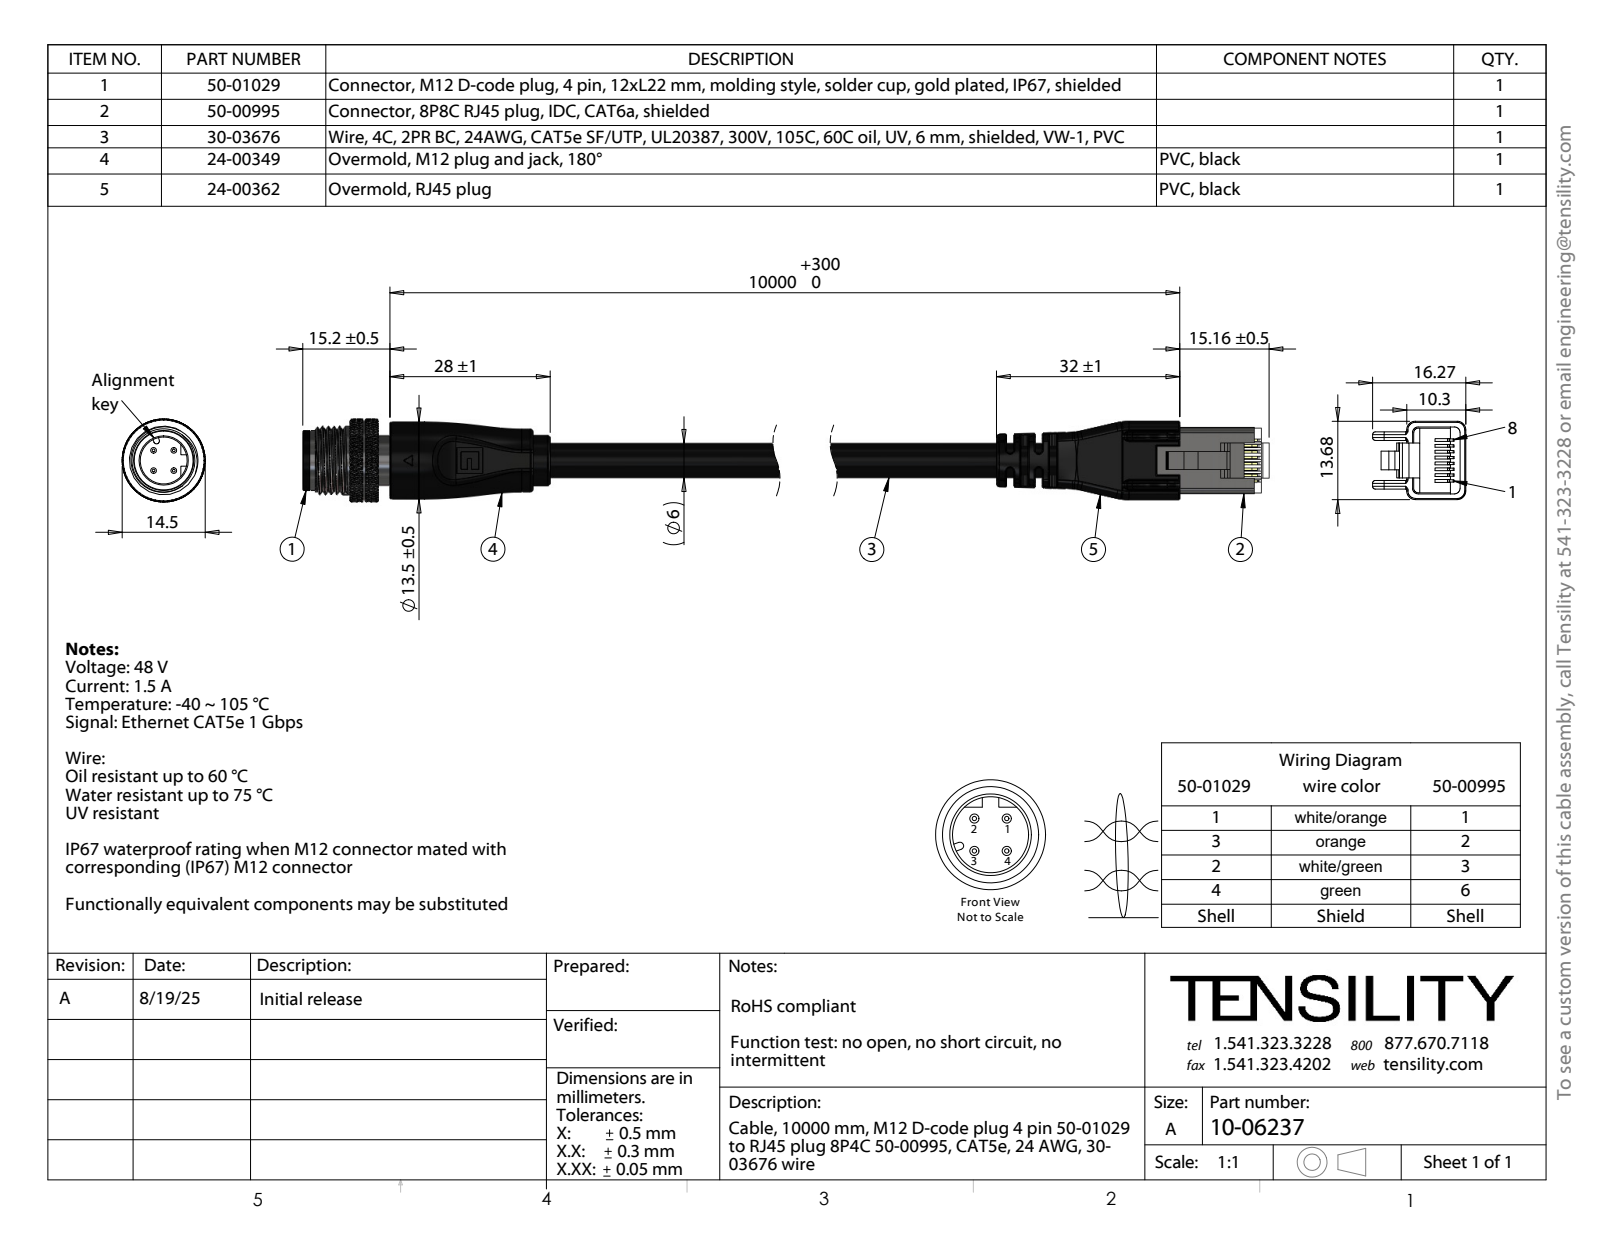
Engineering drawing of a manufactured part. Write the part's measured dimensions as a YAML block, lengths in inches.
part_name: "24-00362; 50-01029-02_默认; 50-00995; 50-01029-03_默认 (+6 more)"
step_written_by: "SolidWorks 2025 (CONFIG_CONTROL_DESIGN)"
units: inches
bodies: {solids: 54, faces: 3209, planar: 470, cylindrical: 811, other: 1928}
overall_size: [9.067, 0.723, 0.571]
volume: 0.849
surface_area: 45.15
round_holes:
  - {diameter: 0.008, count: 28}
  - {diameter: 0.039, count: 4}
  - {diameter: 0.041, count: 4}
  - {diameter: 0.124, count: 1}
  - {diameter: 0.126, count: 1}
  - {diameter: 0.14, count: 1}
  - {diameter: 0.315, count: 1}
  - {diameter: 0.323, count: 1}
  - {diameter: 0.346, count: 1}
  - {diameter: 0.374, count: 1}
round_bosses_or_shafts:
  - {diameter: 0.055, count: 4}
  - {diameter: 0.571, count: 1}
  - {diameter: 0.547, count: 1}
  - {diameter: 0.531, count: 1}
  - {diameter: 0.472, count: 1}
  - {diameter: 0.433, count: 1}
  - {diameter: 0.413, count: 1}
  - {diameter: 0.366, count: 1}
partial_cylinders:
  - {radius: 0.008, count: 11}
  - {radius: 0.02, count: 10}
  - {radius: 0.059, count: 10}
  - {radius: 0.024, count: 8}
  - {radius: 0.039, count: 5}
  - {radius: 0.394, count: 4}
  - {radius: 0.031, count: 2}
  - {radius: 0.045, count: 2}
face_to_face_distances: [0.049, 0.098, 0.039, 0.148, 0.197, 0.366, 0.276, 7.854, 0.499, 0.46]
hole_center_spacings: [0.042, 0.075, 0.082, 0.014, 0.043, 0.067, 0.071, 0.089]
